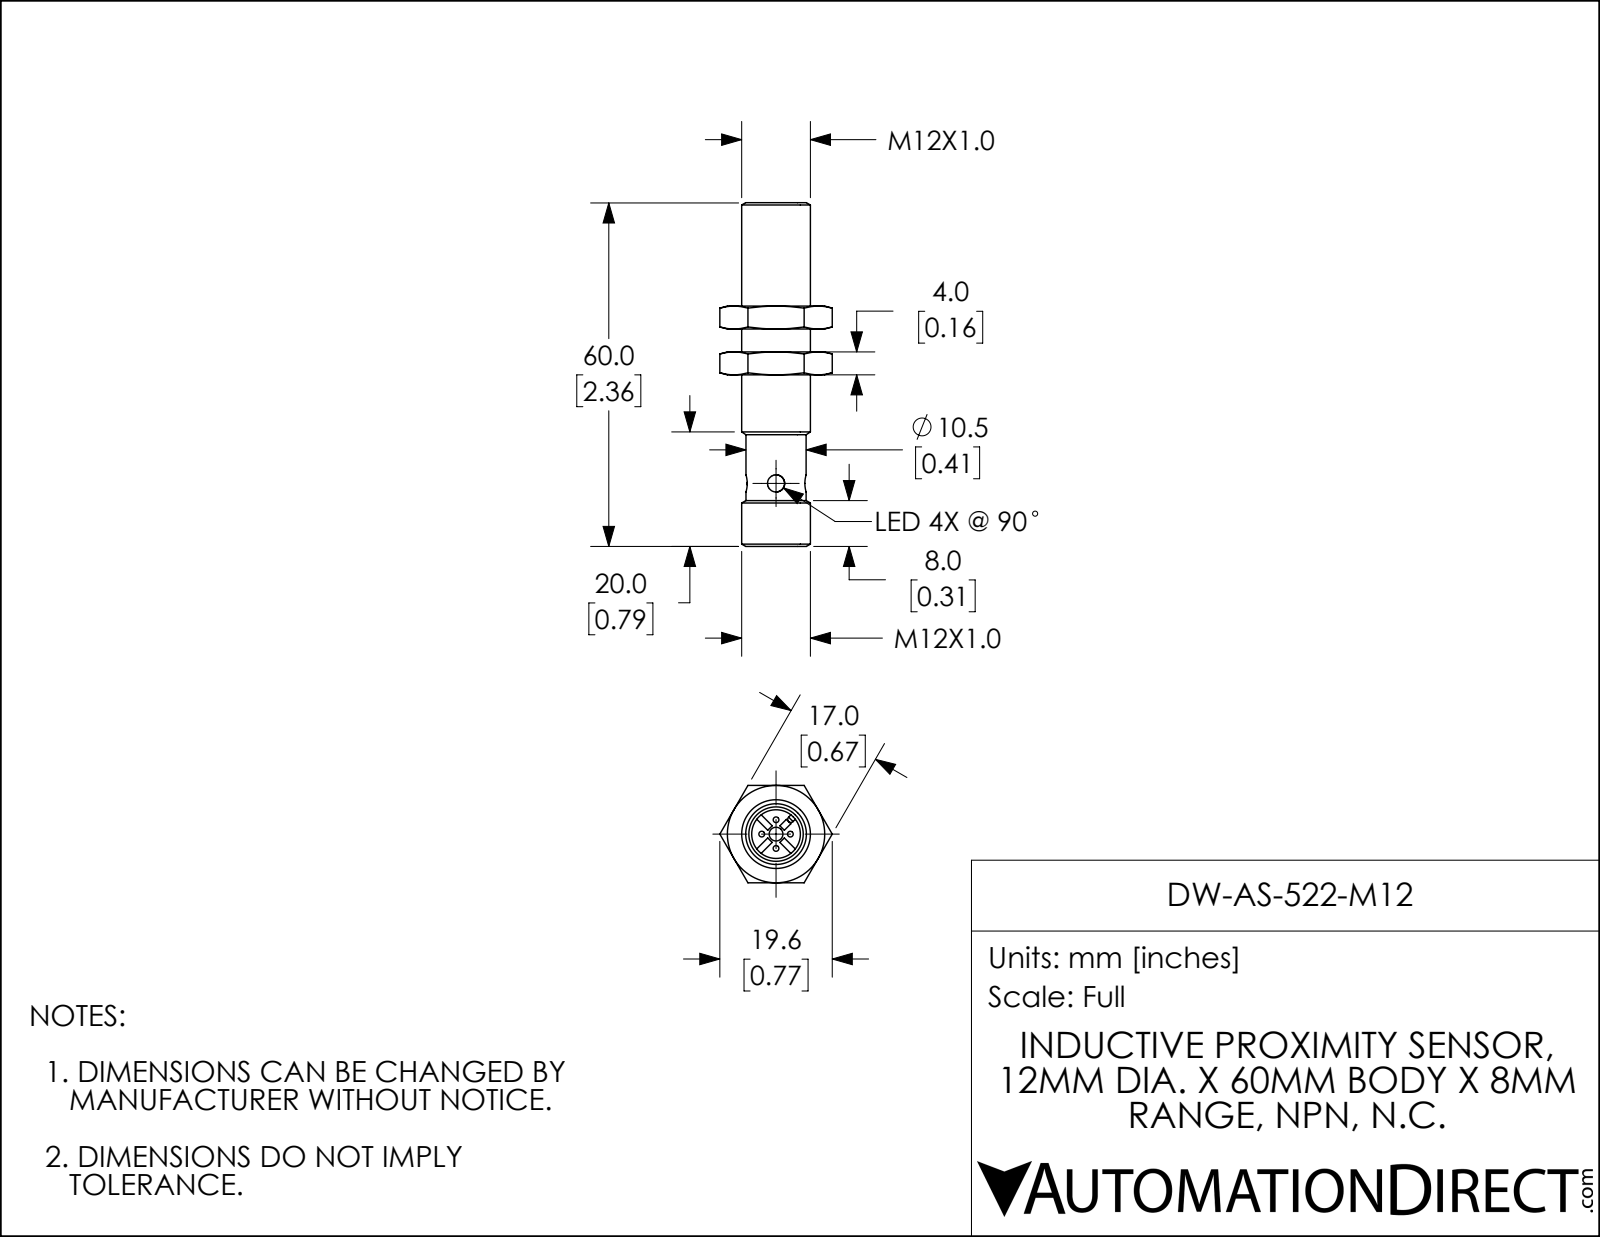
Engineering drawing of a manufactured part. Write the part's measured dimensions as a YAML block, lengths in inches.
part_name: "DW-AS-522-M12"
step_written_by: "SolidWorks 2018 (AUTOMOTIVE_DESIGN)"
units: inches
bodies: {solids: 3, faces: 104, planar: 46, cylindrical: 19, other: 39}
overall_size: [2.362, 0.773, 0.669]
volume: 0.439
surface_area: 6.386
round_holes:
  - {diameter: 0.118, count: 2}
  - {diameter: 0.094, count: 1}
  - {diameter: 0.335, count: 1}
  - {diameter: 0.415, count: 1}
  - {diameter: 0.43, count: 1}
round_bosses_or_shafts:
  - {diameter: 0.039, count: 4}
  - {diameter: 0.472, count: 1}
  - {diameter: 0.413, count: 1}
  - {diameter: 0.406, count: 1}
partial_cylinders:
  - {radius: 0.022, count: 2}
face_to_face_distances: [0.157, 0.315, 0.669, 0.472, 1.183, 1.026, 0.868, 0.711, 0.837, 0.994]
